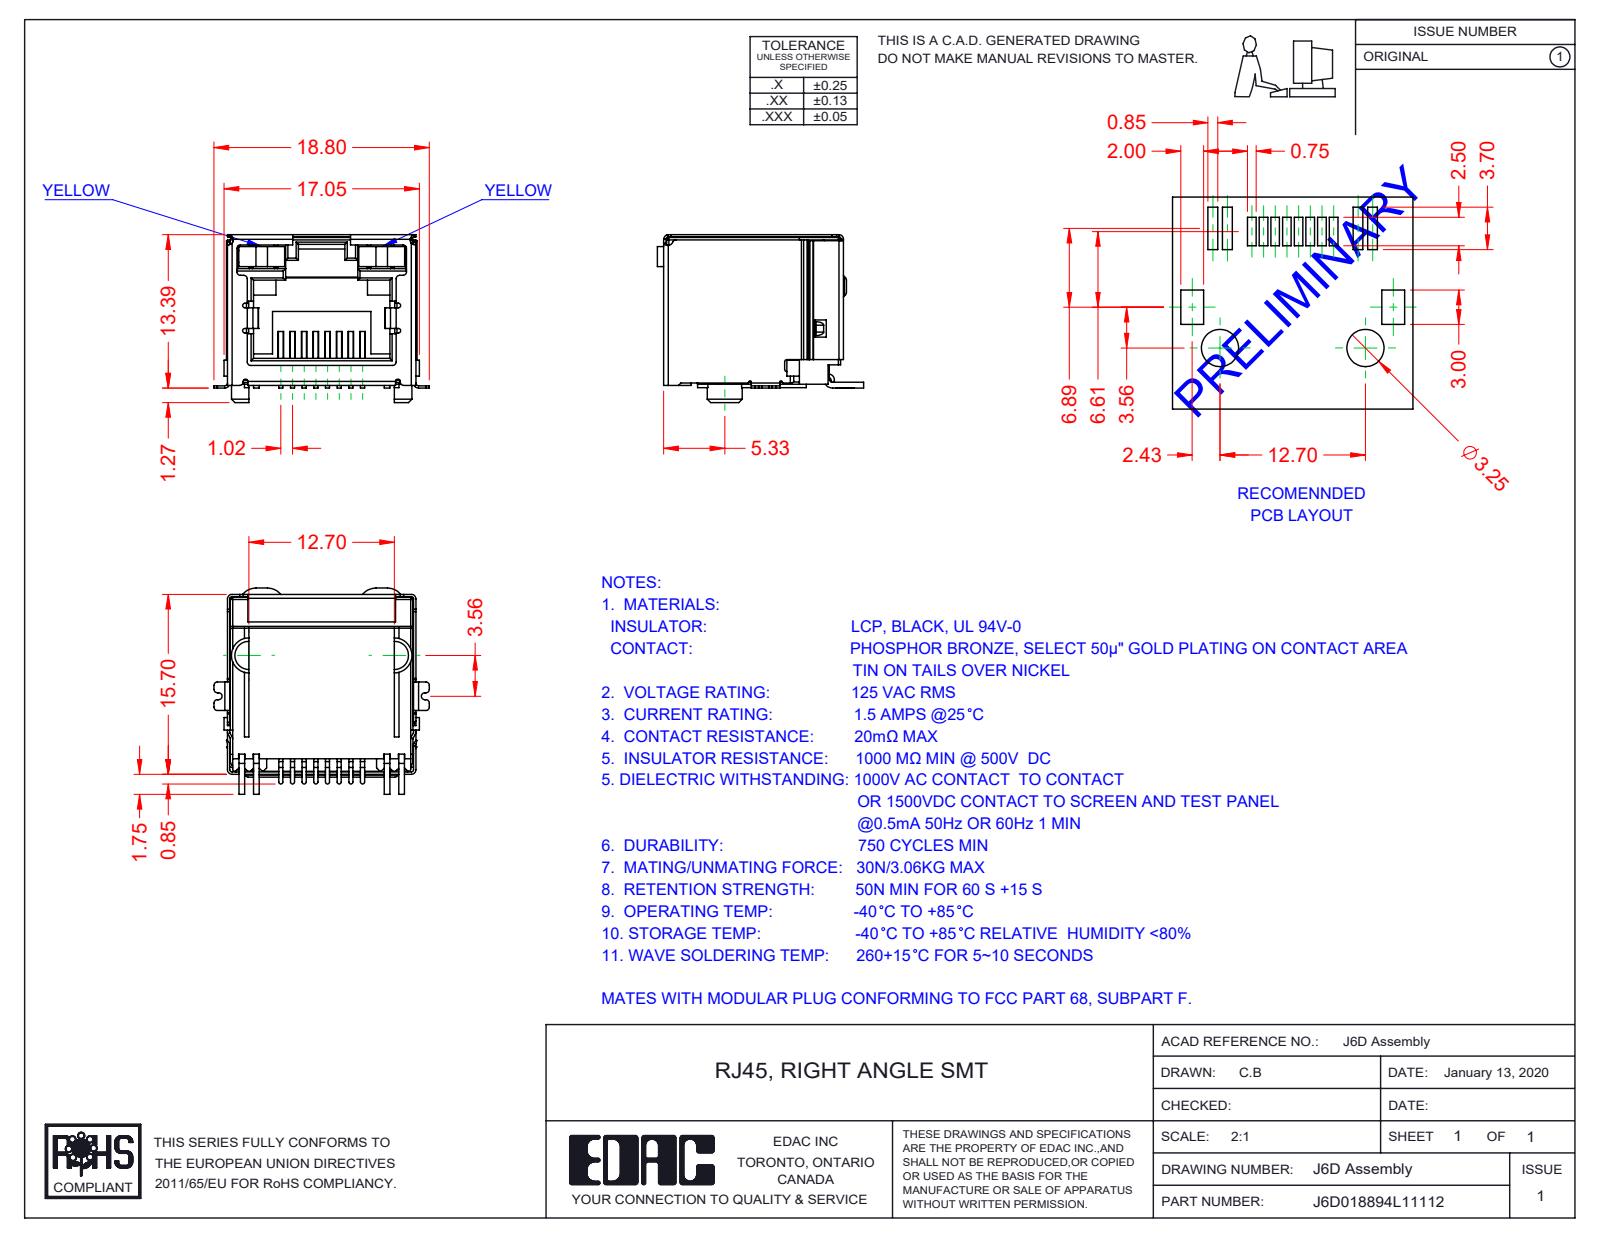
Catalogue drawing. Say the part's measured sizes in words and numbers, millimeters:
The part is named "6D Shield_LED - No EMI; 6D LED RH_1-Yellow; 6D Insulator; J6D018894L11112 (+2 more)". Its 3-D file was written by "SolidWorks 2016 (CONFIG_CONTROL_DESIGN)". It is 12 solids with 893 faces: 644 planar, 216 cylindrical and 33 other. Overall it measures 18.8 by 18 by 14.65 millimeters. Its volume is 1 804 cubic millimeters and its surface area 4 898 square millimeters. Partial cylindrical surfaces (rounded edges, fillets, slot ends): 39 of radius 0.3, 37 of radius 0.2, 16 of radius 0.4, 12 of radius 0.1, 8 of radius 0.15, 8 of radius 0.18, 6 of radius 0.5, 5 of radius 1.5. The main face-to-face distances are 16, 16.25, 16.2, 2.25, 1, 15.95, 16.05, 12.8, 0.45, 16.45.
